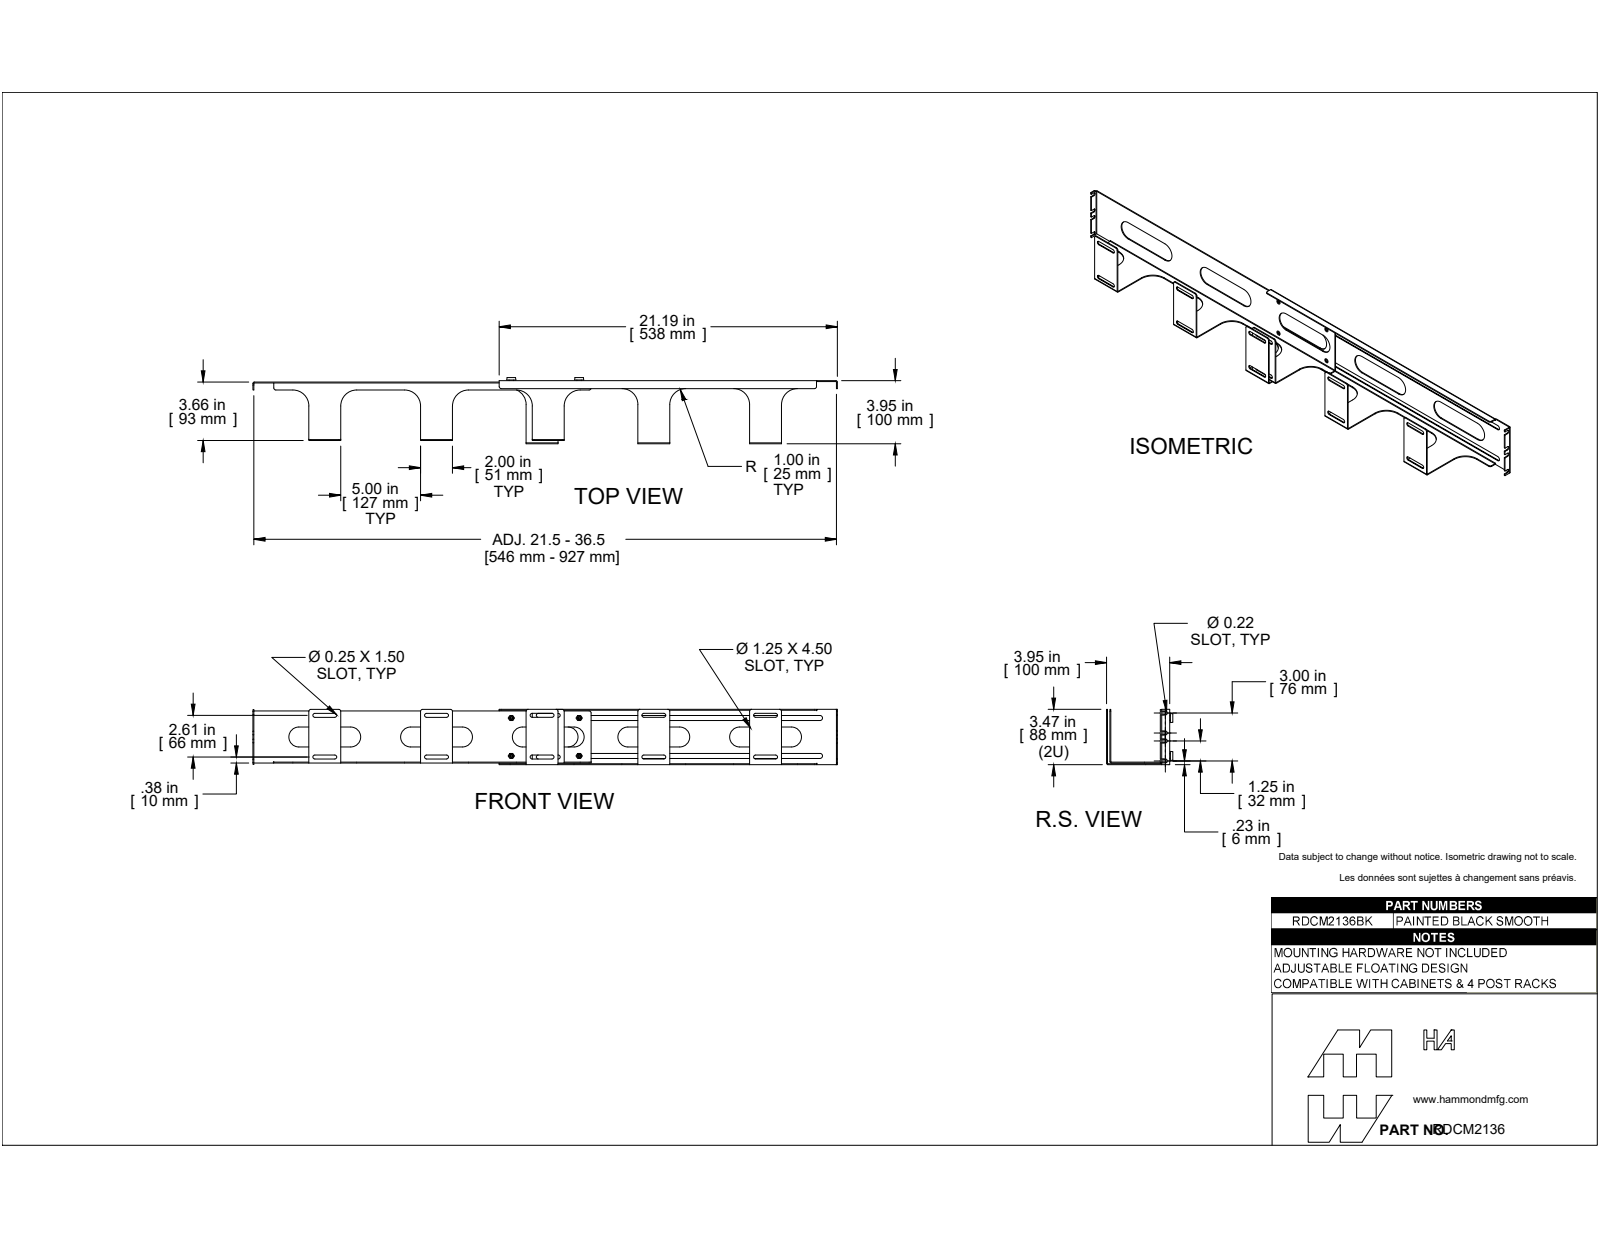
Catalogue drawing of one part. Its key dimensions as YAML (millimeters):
part_name: "RDCM2136BK"
step_written_by: "SolidWorks 2019 (AUTOMOTIVE_DESIGN)"
units: millimeters
bodies: {solids: 18, faces: 449, planar: 266, cylindrical: 131, other: 52}
overall_size: [930, 105.3, 88.1]
volume: 192500
surface_area: 280600
round_holes:
  - {diameter: 4, count: 4}
  - {diameter: 7.1, count: 4}
  - {diameter: 8, count: 4}
round_bosses_or_shafts:
  - {diameter: 13, count: 4}
  - {diameter: 7, count: 4}
  - {diameter: 4.8, count: 4}
  - {diameter: 3.8, count: 4}
partial_cylinders:
  - {radius: 3.2, count: 45}
  - {radius: 15.9, count: 12}
  - {radius: 25.4, count: 12}
  - {radius: 0.7, count: 7}
  - {radius: 2.2, count: 7}
  - {radius: 2.8, count: 4}
  - {radius: 1.5, count: 2}
  - {radius: 4, count: 2}
face_to_face_distances: [1.4, 2.2, 1.4, 0.8, 3.7, 96.8, 99, 2.6, 1.2, 4.1]
hole_center_spacings: [60.3, 108, 123.7]
